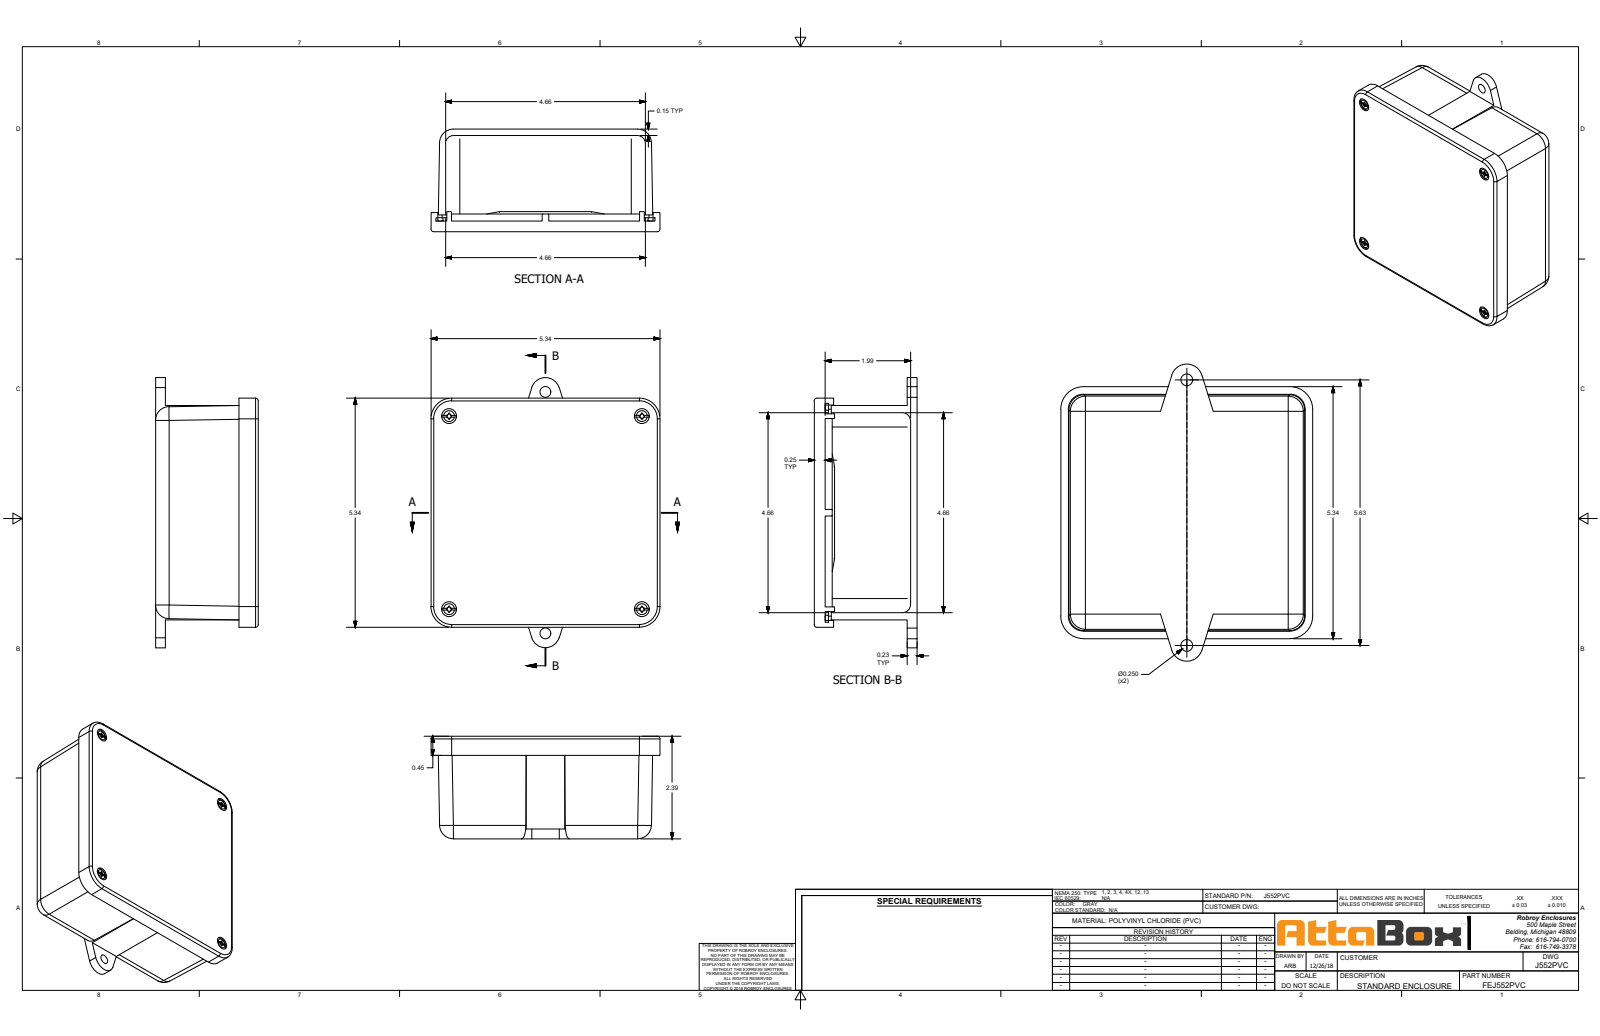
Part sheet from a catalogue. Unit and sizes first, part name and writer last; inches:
Units: inches
Overall size (bounding box): 6.3 × 5.34 × 2.394
Round holes (diameter × count): ⌀0.25 ×6, ⌀0.13 ×4, ⌀0.185 ×4, ⌀0.187 ×4, ⌀0.2 ×4, ⌀0.223 ×4, ⌀0.335 ×4, ⌀0.345 ×4
Round bosses / shafts (diameter × count): ⌀0.354 ×4, ⌀0.177 ×4, ⌀0.325 ×3, ⌀0.187 ×2, ⌀0.325 ×1
Partial cylindrical surfaces — rounded edges, fillets, slot ends (radius × count): R0.015 ×40, R0.031 ×20, R0.005 ×16, R0.016 ×12, R0.32 ×12, R0.047 ×8, R0.062 ×6, R0.063 ×6
Main face-to-face distances: 0.25, 2.144, 2.394, 0.15, 1.994, 2.244, 4.66, 0.34, 5, 2.065
Hole centre spacings: 4.5, 2.32, 5.542, 2.32, 4.5, 5.543, 6.364, 6.364
Volume: 18.12 in³ · Surface area: 218.3 in²
Bodies: 15 solids, 649 faces (315 planar, 234 cylindrical, 100 other)
Part name (STEP PRODUCT): J552PVC
STEP written by: SolidWorks 2018 (AUTOMOTIVE_DESIGN)
